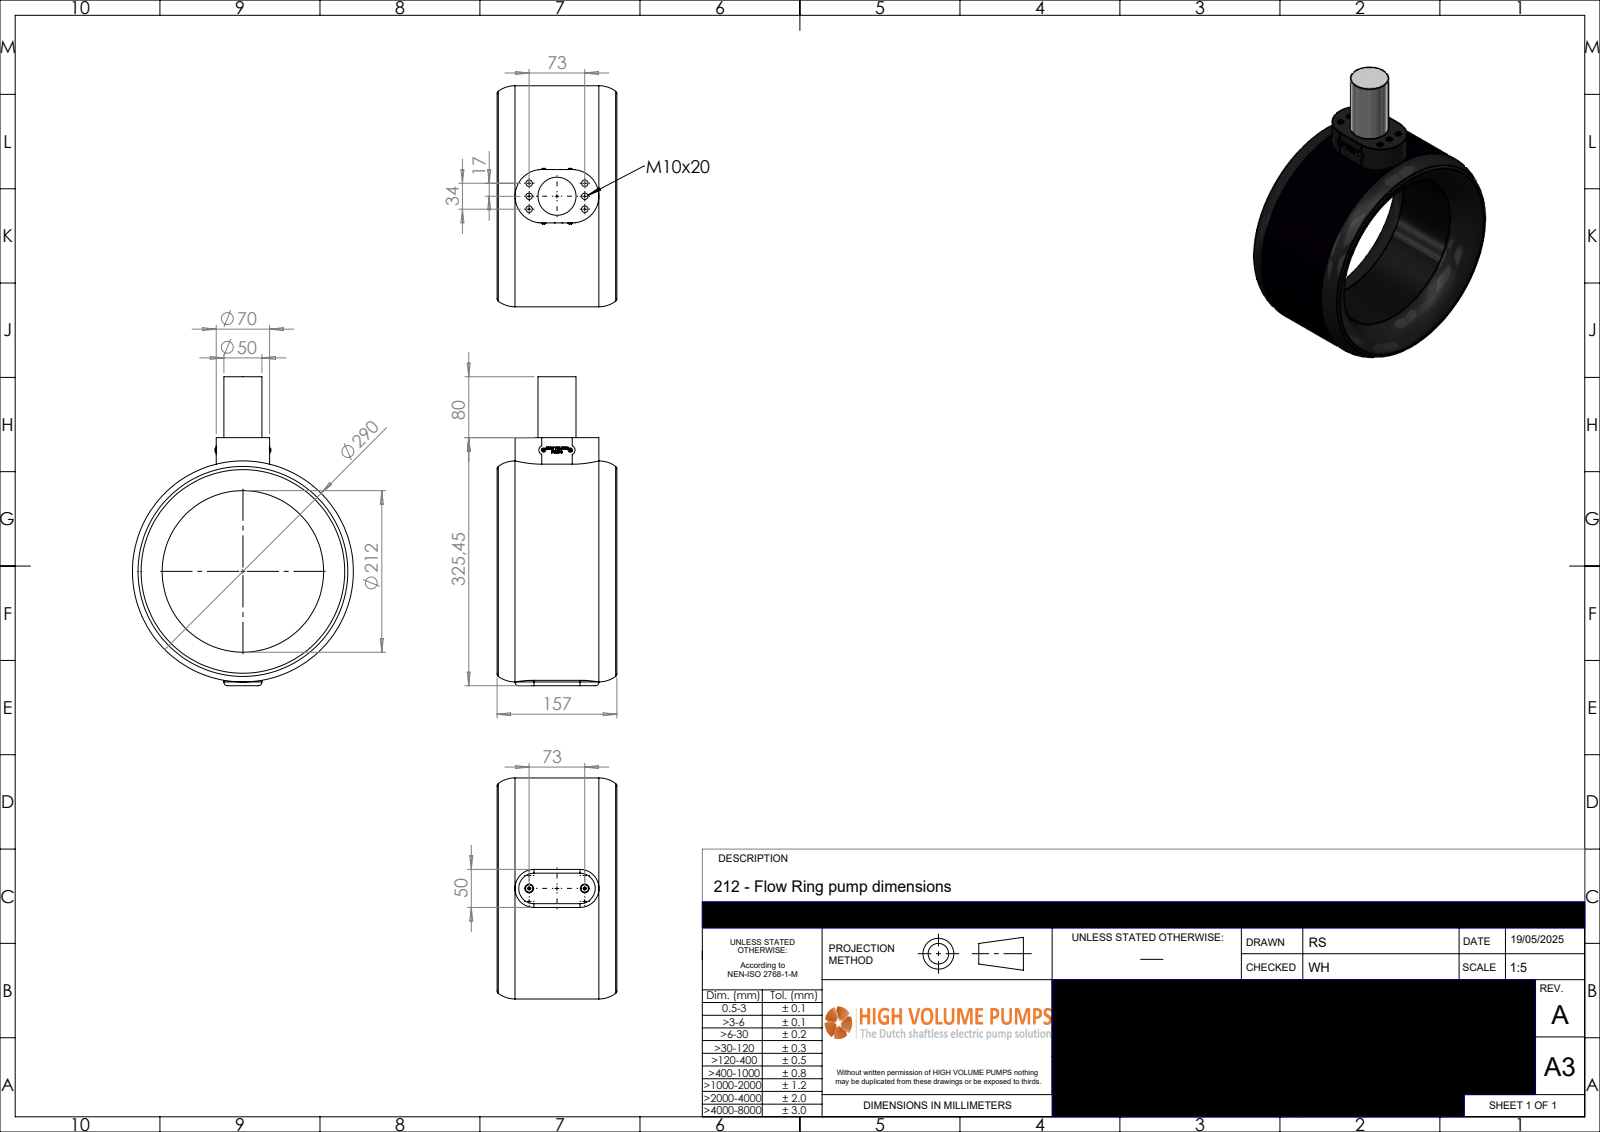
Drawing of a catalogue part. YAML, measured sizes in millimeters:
part_name: "P-212-030-rev-A-FR"
step_written_by: "SolidWorks 2024 (AUTOMOTIVE_DESIGN)"
units: millimeters
bodies: {solids: 1, faces: 554, planar: 369, cylindrical: 41, other: 144}
overall_size: [405.45, 290, 157.28]
volume: 4750000
surface_area: 306405
round_holes:
  - {diameter: 8.5, count: 6}
  - {diameter: 3.5, count: 2}
  - {diameter: 212, count: 1}
round_bosses_or_shafts:
  - {diameter: 9.64, count: 2}
  - {diameter: 5.7, count: 2}
  - {diameter: 3, count: 2}
  - {diameter: 290, count: 1}
  - {diameter: 50, count: 1}
partial_cylinders:
  - {radius: 25, count: 4}
  - {radius: 5, count: 2}
  - {radius: 6.25, count: 2}
  - {radius: 35, count: 2}
face_to_face_distances: [325.45, 405.45, 80, 70, 300, 25.45, 105.45, 10, 60, 50]
hole_center_spacings: [17, 74.95, 73, 34, 80.53, 35]
